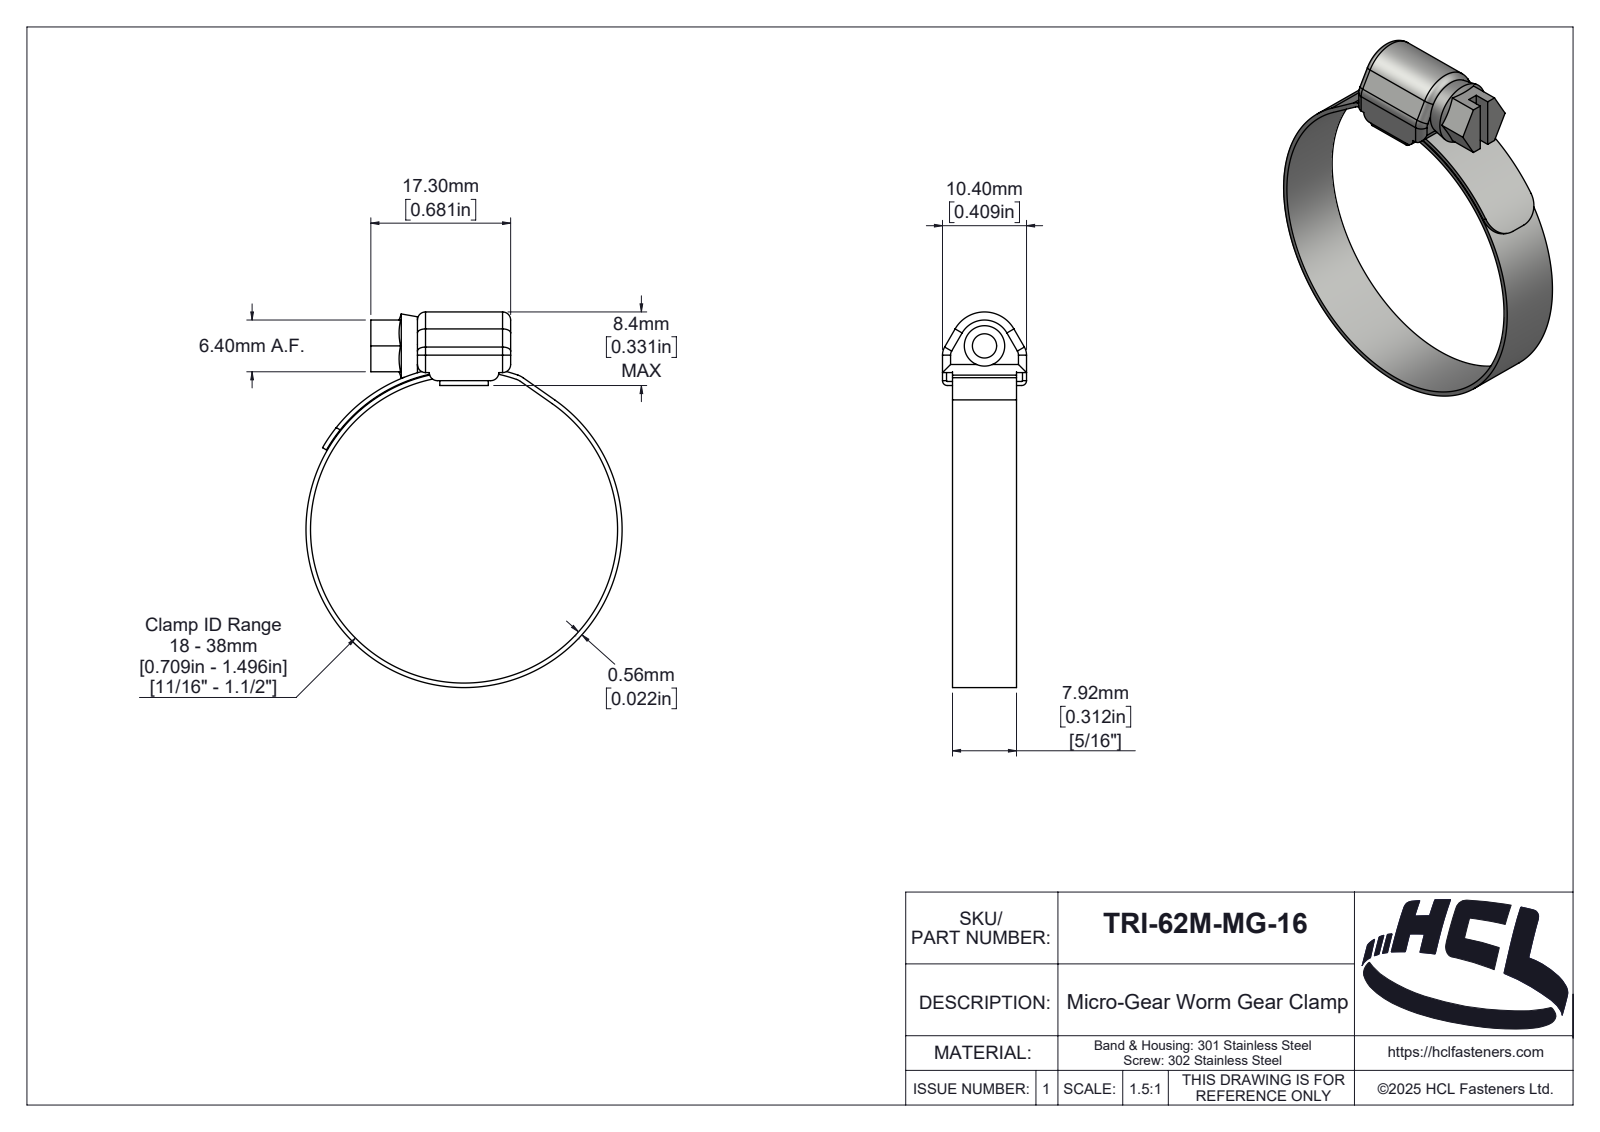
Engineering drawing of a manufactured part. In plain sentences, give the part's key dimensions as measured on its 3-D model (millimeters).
The part is named "TRI-62M-MG-16". Its 3-D file was written by "SolidWorks 2025 (AUTOMOTIVE_DESIGN)". It is 3 solids with 186 faces: 38 planar, 87 cylindrical and 61 other. Overall it measures 46.46 by 39.12 by 10.4 millimeters. Its volume is 1 573 cubic millimeters and its surface area 3 580 square millimeters. Round holes: 1 of diameter 5, 1 of diameter 38. Round bosses or shafts: 1 of diameter 39.12. Partial cylindrical surfaces (rounded edges, fillets, slot ends): 12 of radius 1, 3 of radius 2, 2 of radius 0.1, 2 of radius 0.6, 2 of radius 3, 1 of radius 0.25, 1 of radius 1.01, 1 of radius 1.26. The main face-to-face distances are 1.1, 7.92, 0.5, 1.24, 9.16, 1.6, 0.56, 6.2, 10.4, 5.76.
